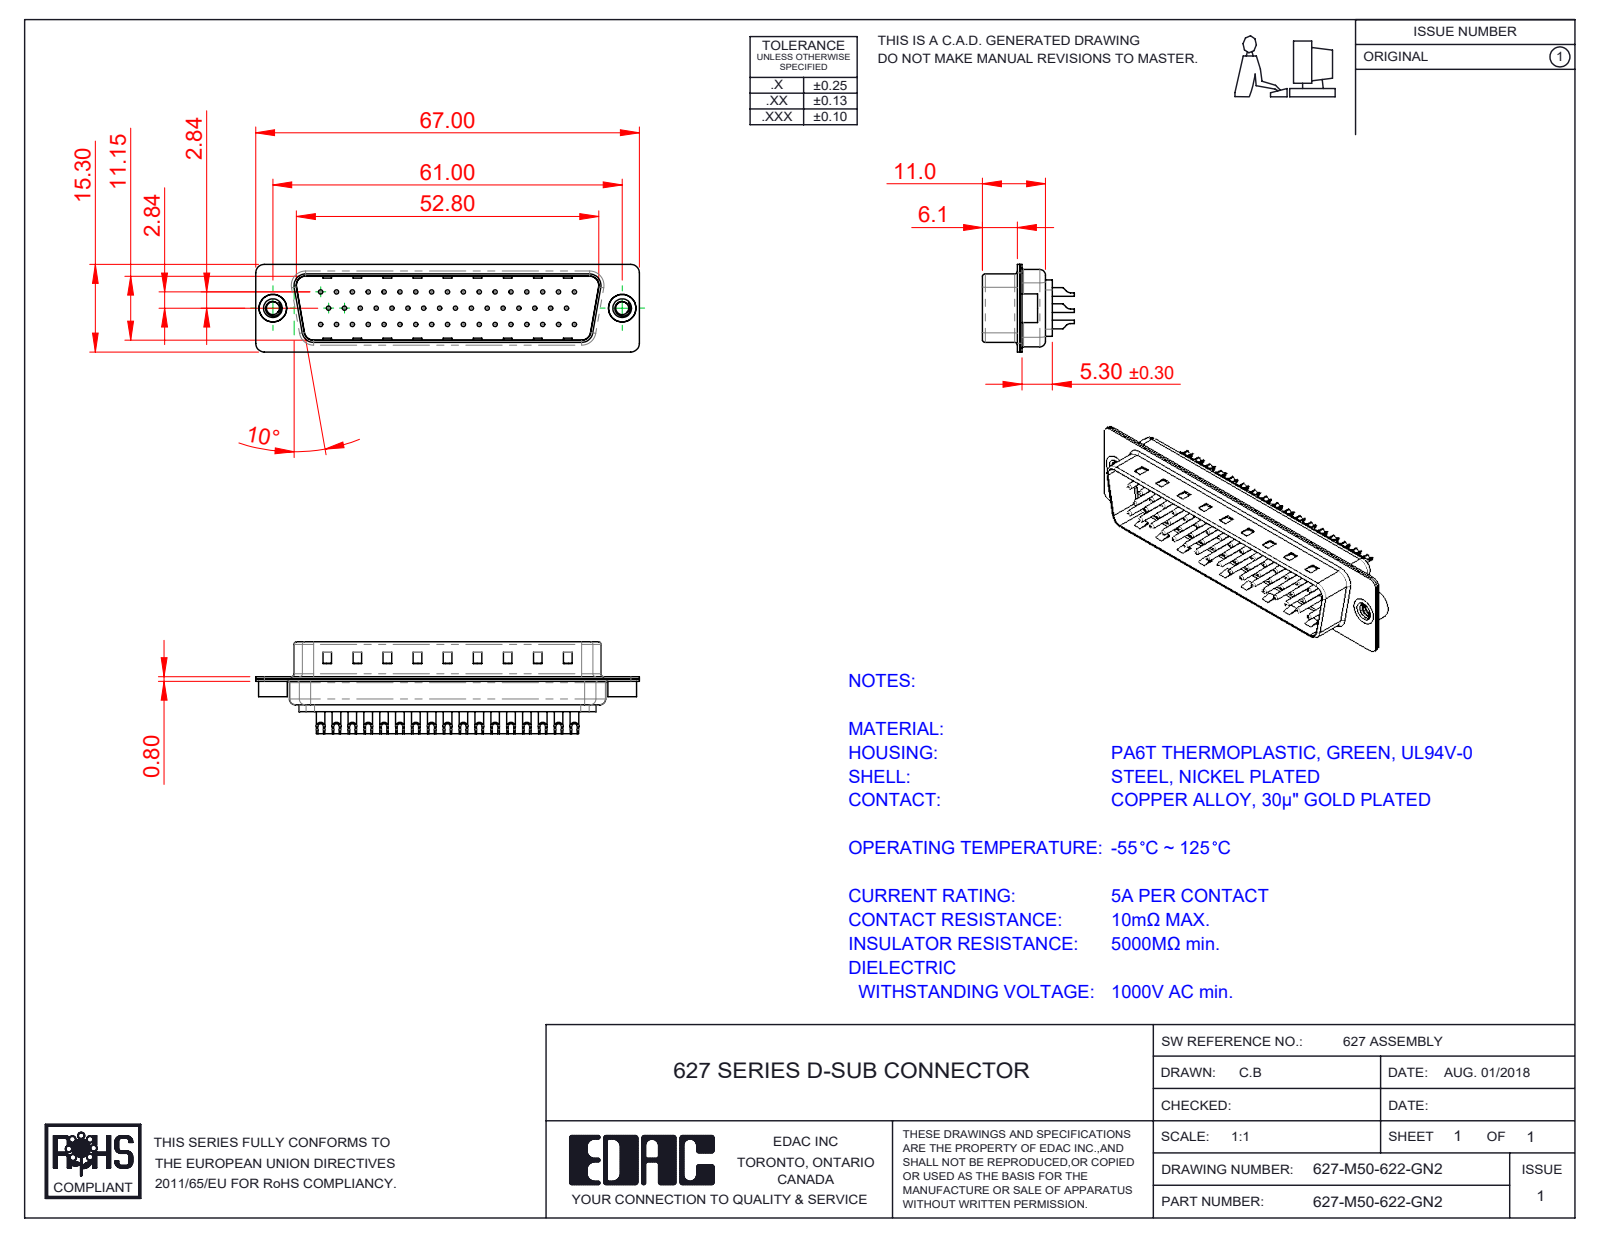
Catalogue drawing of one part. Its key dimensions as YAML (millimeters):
part_name: "627M Shell Front_50 Contacts; 627M Contact Row 2_22L; 627M 4-40 Threaded Rivet; 627-M50-622-GN2 (+4 more)"
step_written_by: "SolidWorks 2020 (CONFIG_CONTROL_DESIGN)"
units: millimeters
bodies: {solids: 55, faces: 2262, planar: 653, cylindrical: 941, other: 668}
overall_size: [67, 16.05, 15.3]
volume: 4639
surface_area: 11168
round_holes:
  - {diameter: 0.75, count: 50}
  - {diameter: 1, count: 50}
  - {diameter: 1.6, count: 50}
  - {diameter: 2, count: 50}
  - {diameter: 2.26, count: 2}
  - {diameter: 4, count: 2}
  - {diameter: 4.8, count: 2}
round_bosses_or_shafts:
  - {diameter: 1.5, count: 50}
  - {diameter: 5, count: 2}
  - {diameter: 4.9, count: 2}
partial_cylinders:
  - {radius: 1.5, count: 16}
  - {radius: 2, count: 12}
  - {radius: 0.5, count: 8}
  - {radius: 1.6, count: 8}
  - {radius: 1, count: 7}
  - {radius: 0.25, count: 4}
  - {radius: 0.6, count: 4}
  - {radius: 0.65, count: 4}
face_to_face_distances: [0.4, 11.55, 5.7, 6.1, 0.78, 0.77, 12.33, 12.32, 13.1, 5.3]
hole_center_spacings: [3.16, 2.77, 5.54, 8.31, 11.08, 13.85, 16.62, 5.03]
